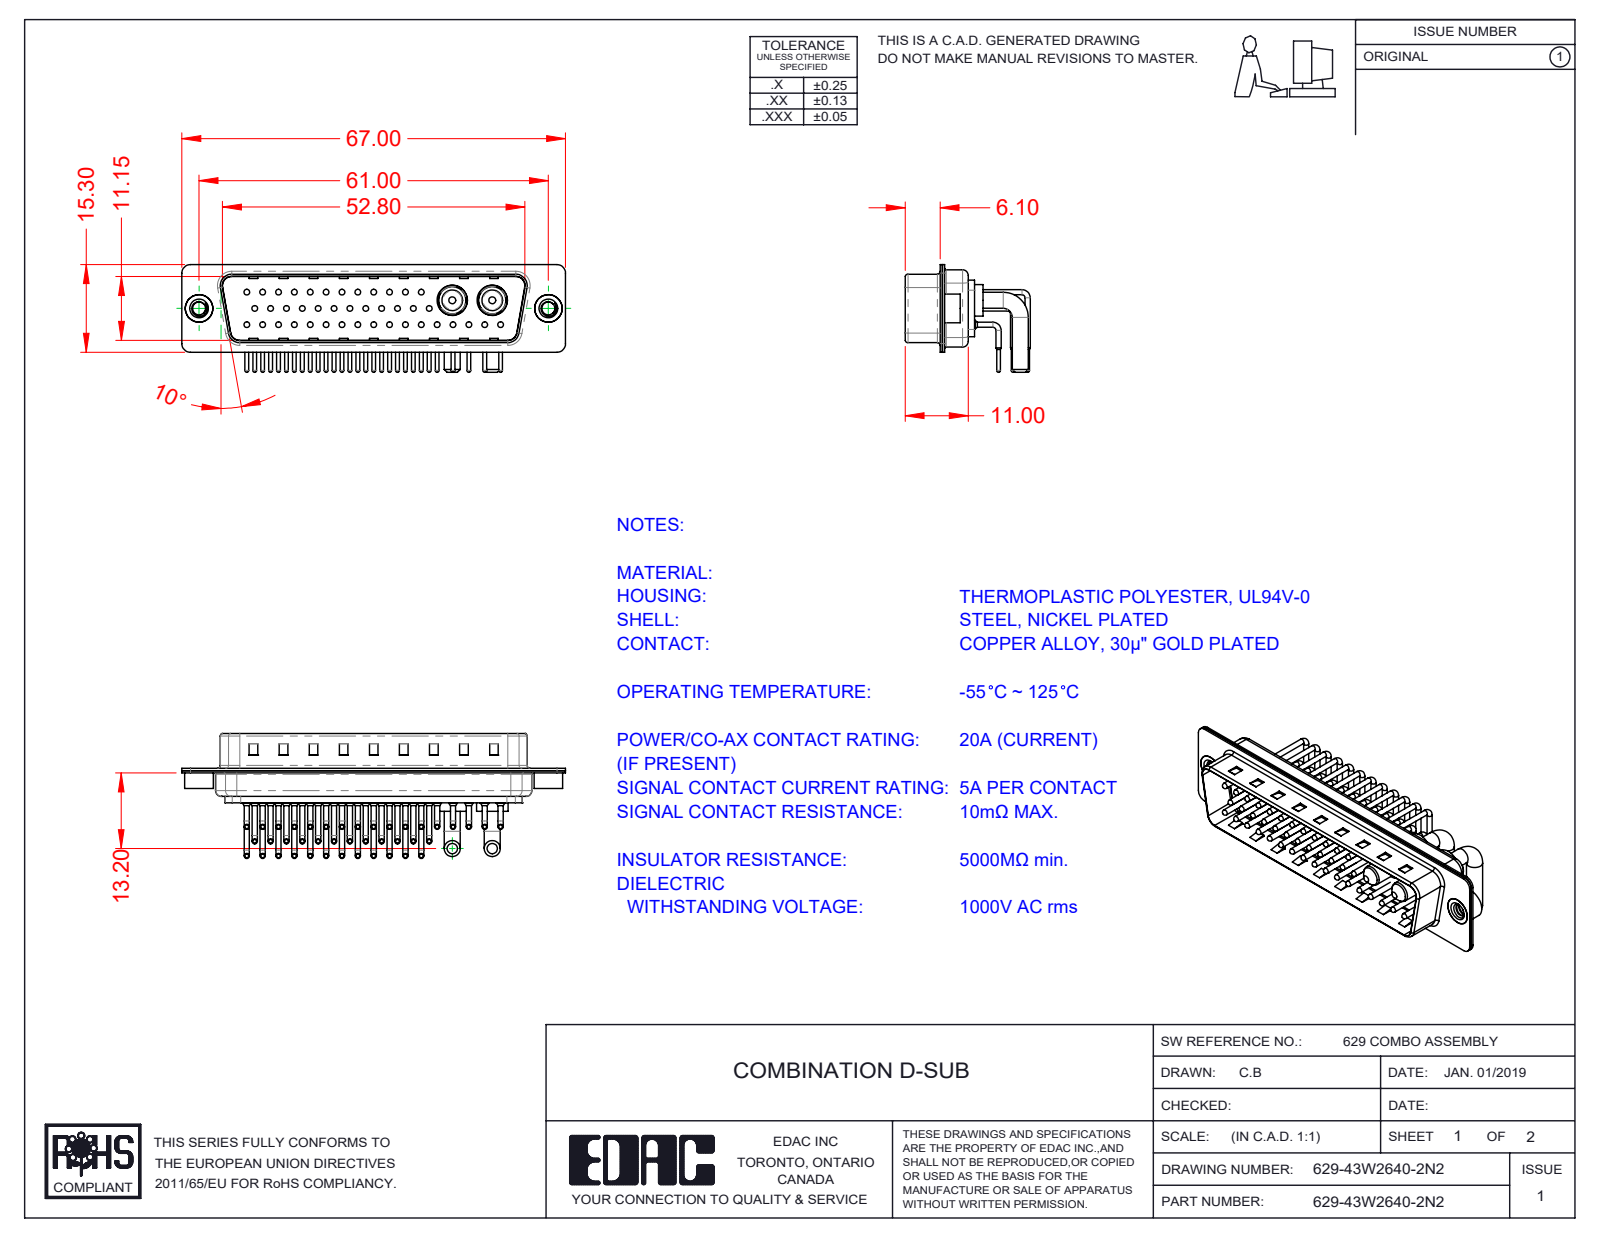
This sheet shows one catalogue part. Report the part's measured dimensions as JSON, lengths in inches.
{"part_name": "629Combo Contact Row 3; 629Combo Contact Row 2_50 Contacts; 629-43W2640-2N2; 629Combo Housing_43W2 (+5 more)", "step_written_by": "SolidWorks 2020 (CONFIG_CONTROL_DESIGN)", "units": "inches", "bodies": {"solids": 50, "faces": 5008, "planar": 2847, "cylindrical": 1659, "other": 502}, "overall_size": [2.638, 0.859, 0.74], "volume_in3": 0.319, "surface_area_in2": 19.54, "round_holes": [[0.03, 41], [0.063, 41], [0.079, 41], [0.089, 2], [0.157, 2], [0.189, 2], [0.191, 2], [0.209, 2]], "round_bosses_or_shafts": [[0.035, 82], [0.059, 41], [0.039, 41], [0.026, 41], [0.11, 4], [0.217, 2], [0.205, 2], [0.197, 2]], "partial_cylinders_radius": [[0.04, 41], [0.059, 16], [0.079, 12], [0.02, 8], [0.063, 8], [0.01, 4], [0.024, 4], [0.026, 4]], "face_to_face_distances": [0.016, 0.455, 0.22, 0.161, 0.236, 0.059, 0.031, 0.03, 0.485, 0.043], "hole_center_spacings": [0.109, 0.218, 0.124, 0.327, 0.436, 0.545, 0.654, 0.763]}
